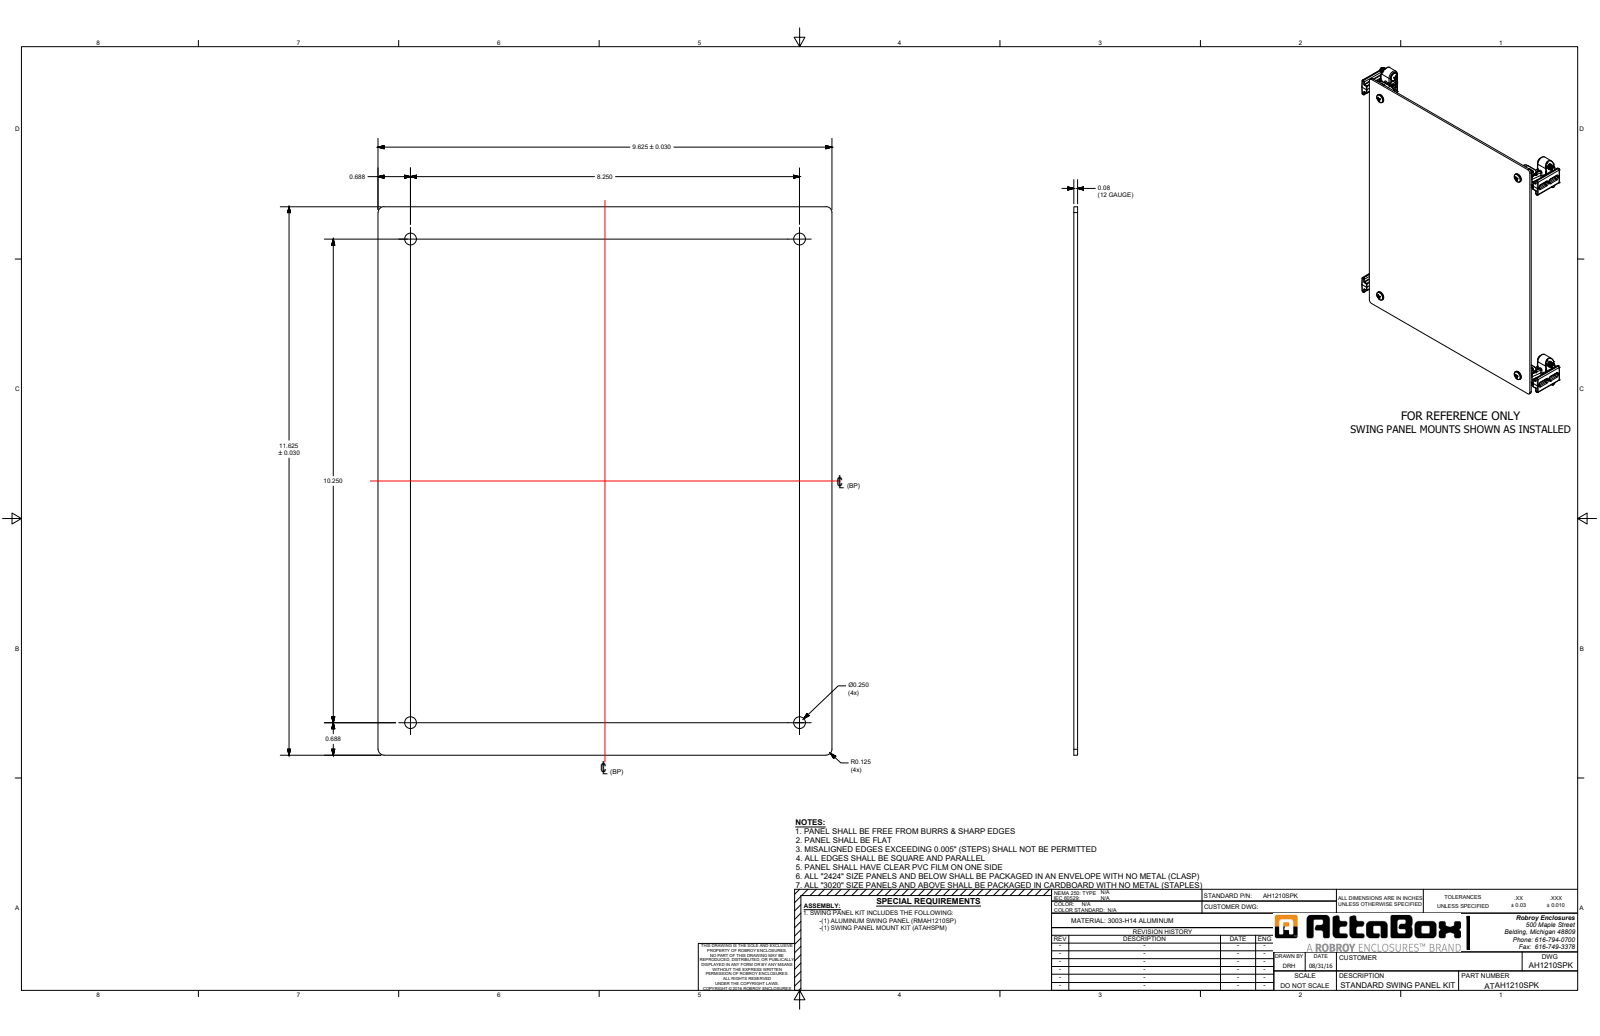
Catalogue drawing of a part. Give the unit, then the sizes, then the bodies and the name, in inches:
Units: inches
Overall size (bounding box): 11.625 × 10.559 × 1.448
Round holes (diameter × count): ⌀0.156 ×8, ⌀0.25 ×8
Round bosses / shafts (diameter × count): ⌀0.373 ×8, ⌀0.262 ×8, ⌀0.19 ×8
Partial cylindrical surfaces — rounded edges, fillets, slot ends (radius × count): R0.035 ×248, R0.02 ×124, R0.065 ×54, R0.015 ×30, R0.045 ×16, R0.05 ×16, R0.025 ×12, R0.9 ×8
Main face-to-face distances: 0.08, 10.25, 0.174, 0.174, 0.5, 0.51, 0.59, 10.559, 0.3, 10.259
Hole centre spacings: 10.25, 0.875, 8.25, 13.157, 9.375, 11.125
Volume: 12.02 in³ · Surface area: 284.5 in²
Bodies: 33 solids, 2010 faces (518 planar, 736 cylindrical, 756 other)
Part name (STEP PRODUCT): AH1210SPK
STEP written by: SolidWorks 2019 (AUTOMOTIVE_DESIGN)
